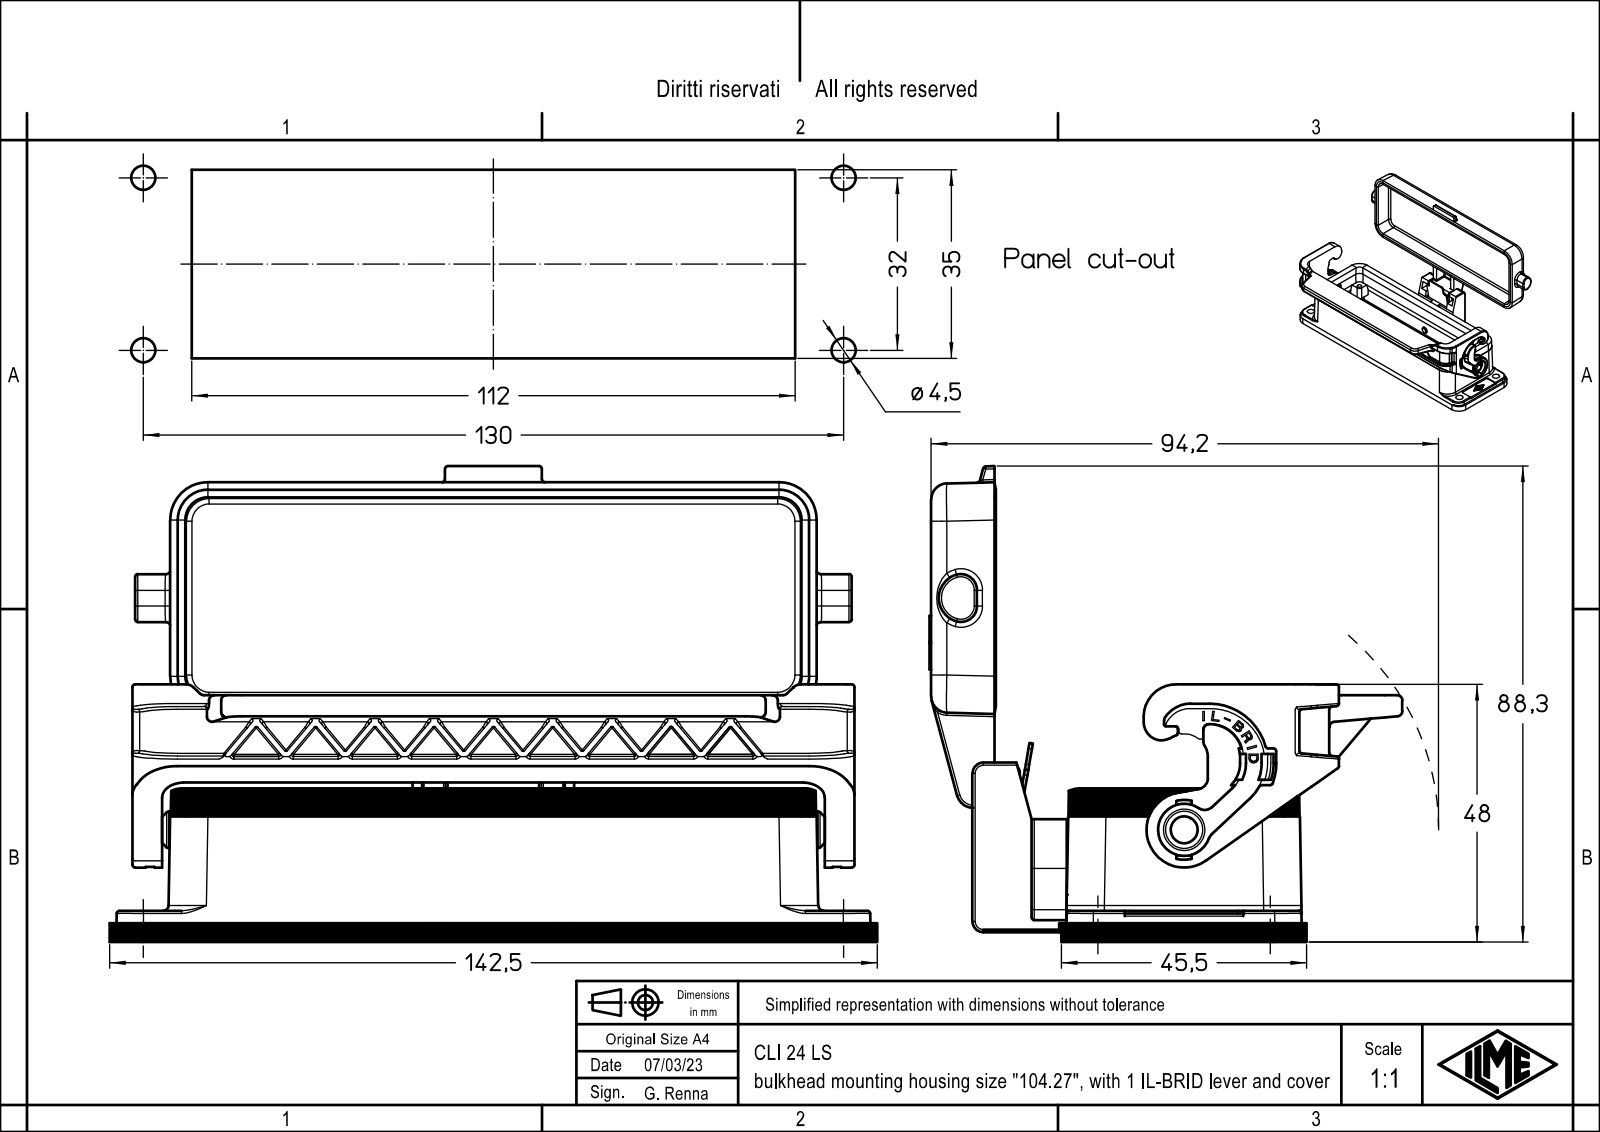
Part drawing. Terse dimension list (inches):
name: CLI 24 LS
written by: Creo Elements/Direct Modeling 20.1B 02-Apr-2019 (C) Parametric Technology GmbH (AUTOMOTIVE_DESIGN)
unit: in
bodies: 1 solid, 1377 faces (863 planar, 391 cylindrical, 123 other)
size: 5.61 × 3.476 × 3.462
volume: 5.184 in³; area: 95 in²
holes: 4× ⌀0.15, 4× ⌀0.177, 1× ⌀0.128, 1× ⌀0.213, 1× ⌀0.303
bosses: 1× ⌀0.331, 1× ⌀0.272, 1× ⌀0.268, 1× ⌀0.205, 1× ⌀0.126
rounds: 32× R0.007, 29× R0.02, 28× R0.039, 27× R0.004, 23× R0.008, 17× R0.013, 17× R0.079, 15× R0.118
face distances: 0.079, 2.752, 0.11, 2.83, 0.119, 1.803, 0.663, 0.138, 1.594, 1.531
hole spacings: 1.26, 5.118, 5.271
